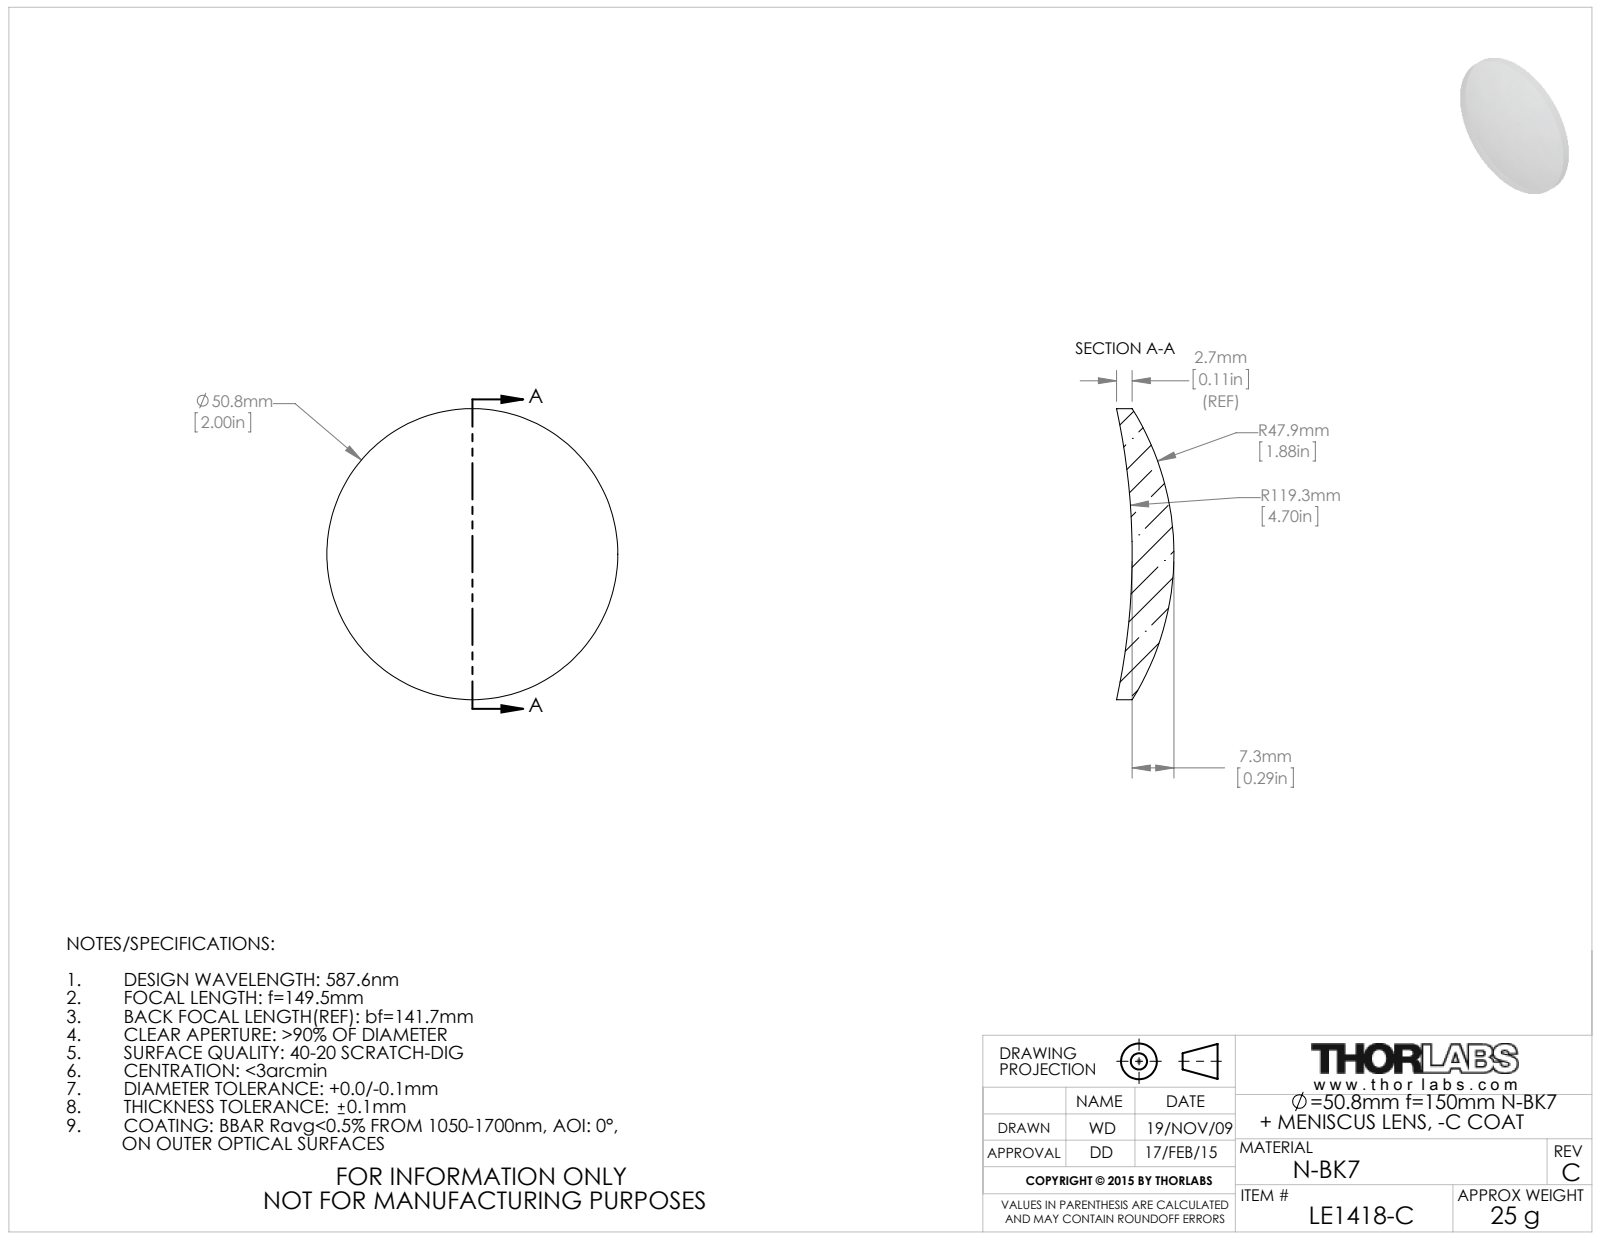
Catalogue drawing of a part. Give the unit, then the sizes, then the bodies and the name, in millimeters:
Units: millimetres
Overall size (bounding box): 50.8 × 50.8 × 10.03
Round bosses / shafts (diameter × count): ⌀50.8 ×1
Volume: 10 347 mm³ · Surface area: 4 680 mm²
Bodies: 1 solid, 6 faces (0 planar, 2 cylindrical, 4 other)
Part name (STEP PRODUCT): 4861-E0W
STEP written by: SolidWorks 2009 (AUTOMOTIVE_DESIGN)
